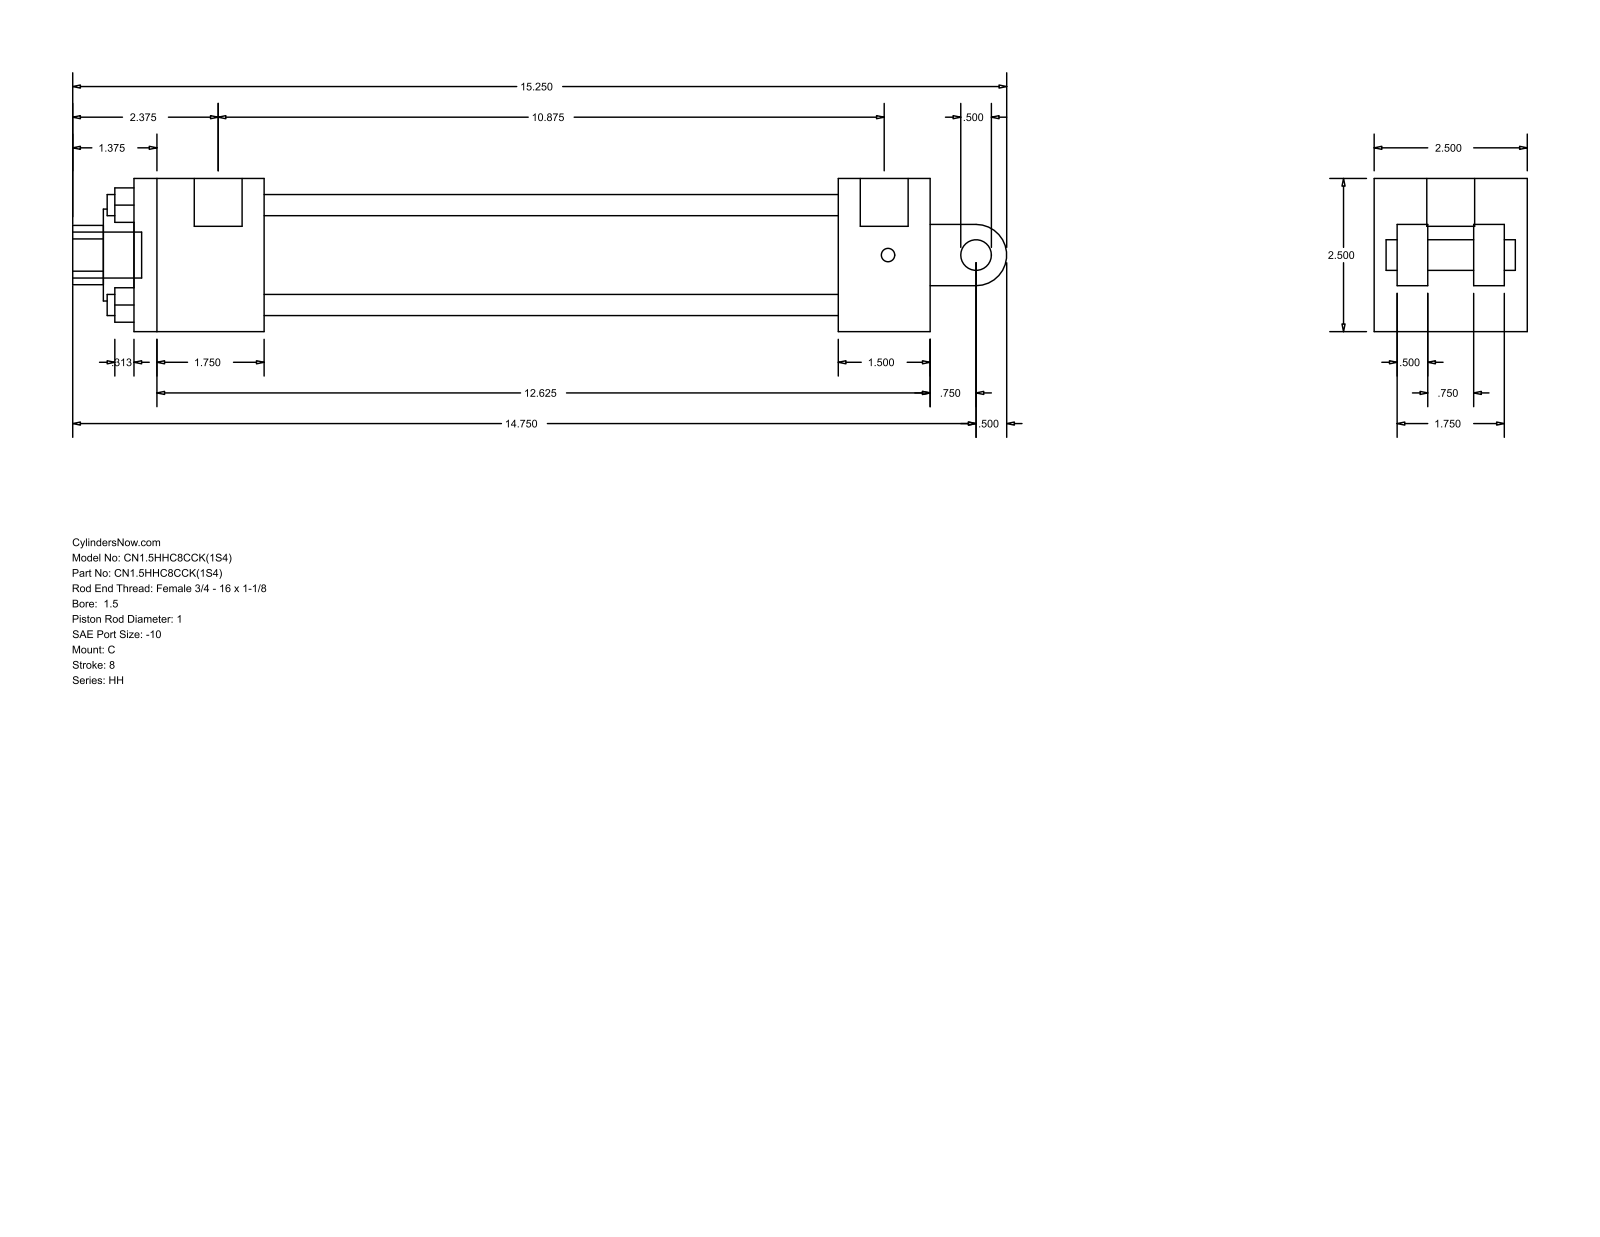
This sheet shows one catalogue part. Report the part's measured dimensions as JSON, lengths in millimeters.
{"part_name": "HH_C__0150_1", "step_written_by": "GSSL Pune (CONFIG_CONTROL_DESIGN)", "units": "millimeters", "bodies": {"solids": 0, "faces": 99, "planar": 70, "cylindrical": 29, "other": 0}, "overall_size": [387.35, 63.5, 63.5], "round_holes": [[8.76, 4], [5.56, 2], [19.84, 1], [25.4, 1], [38.1, 1], [44.45, 1]], "round_bosses_or_shafts": [[5.56, 2], [19.84, 1], [19.05, 1], [12.7, 1]], "partial_cylinders_radius": [[12.29, 1], [12.7, 1]], "face_to_face_distances": [63.5, 53.98, 238.12, 276.22, 38.1, 292.1, 330.2, 12.7, 9.52, 22.22], "hole_center_spacings": [29.27, 41.4, 58.55, 1.59]}
